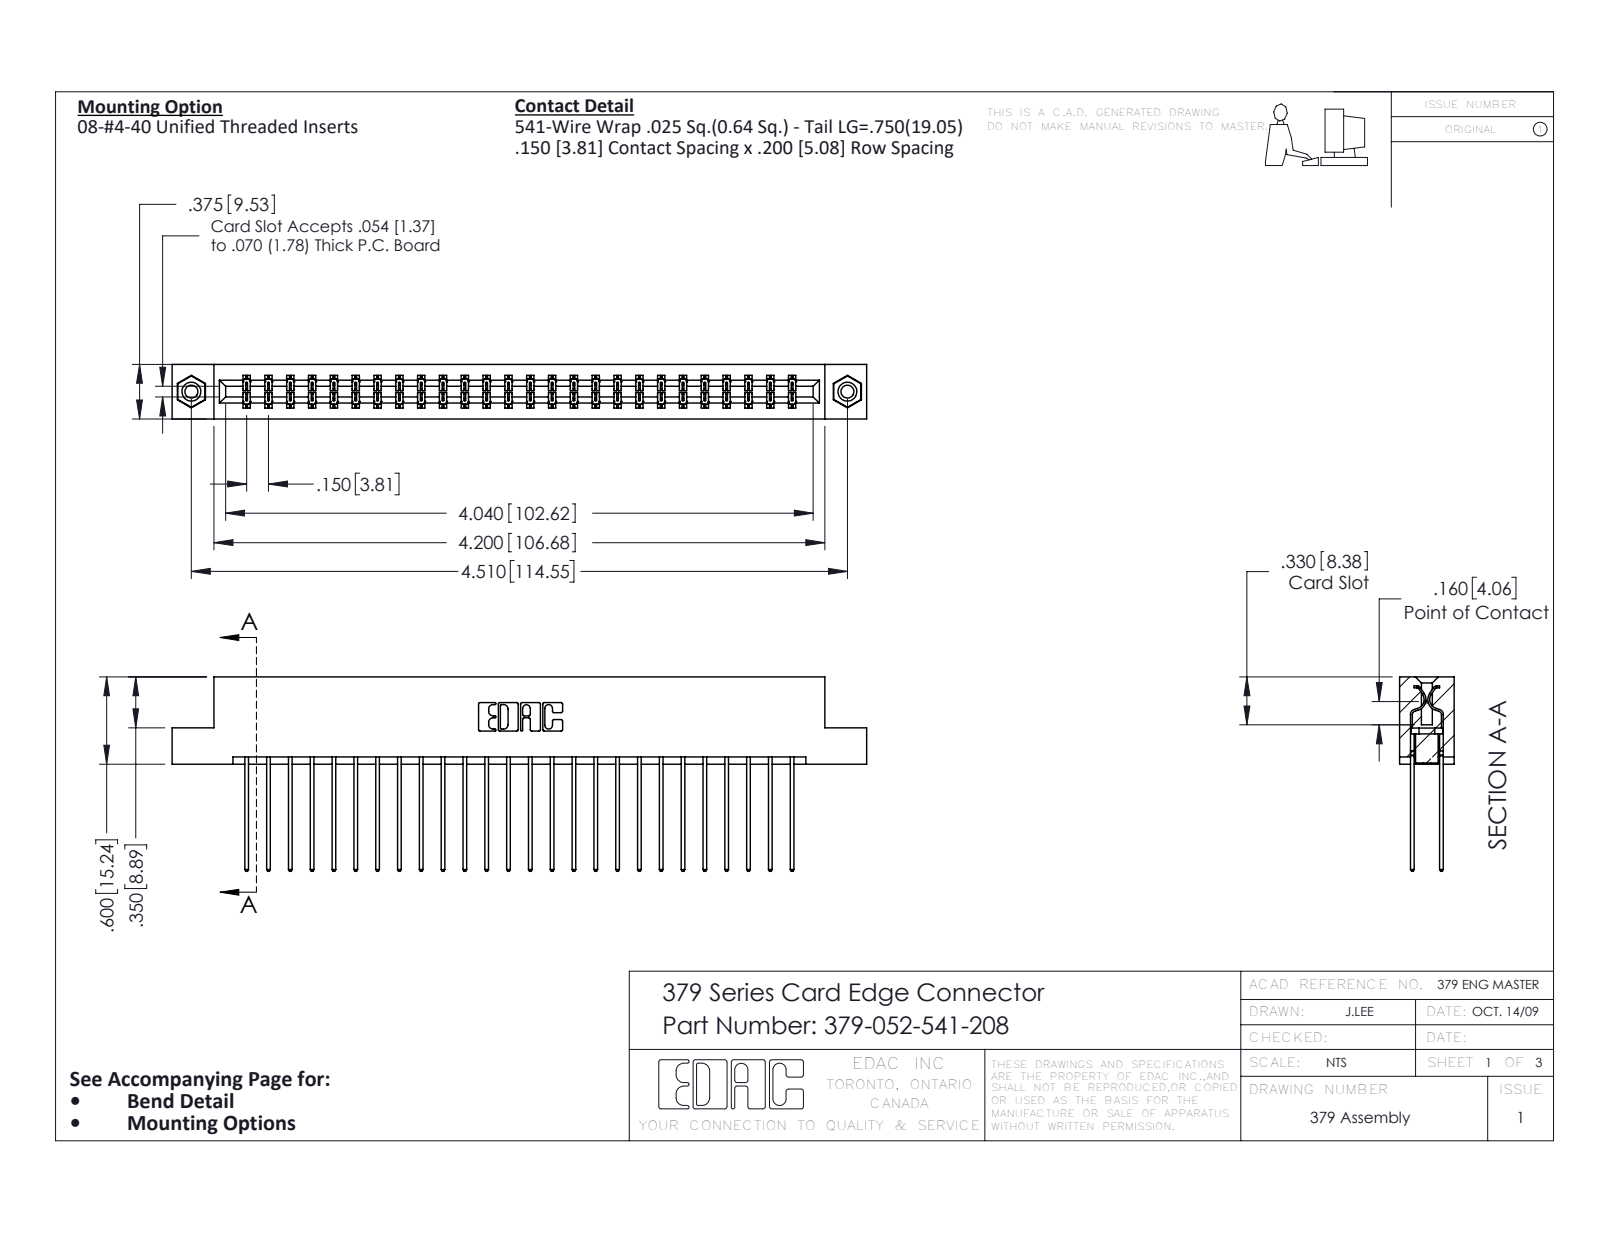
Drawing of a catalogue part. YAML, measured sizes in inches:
part_name: "379 Part_Flush - .156 Dia - TI; 345-250-001_345-250-003-102; 379-052-541-208; 345-292-001_345-293-141"
step_written_by: "SolidWorks 2016 (CONFIG_CONTROL_DESIGN)"
units: inches
bodies: {solids: 55, faces: 2878, planar: 1974, cylindrical: 888, other: 16}
overall_size: [4.775, 1.337, 0.375]
volume: 0.794
surface_area: 24.79
round_holes:
  - {diameter: 0.089, count: 2}
  - {diameter: 0.125, count: 2}
  - {diameter: 0.156, count: 2}
round_bosses_or_shafts:
  - {diameter: 0.155, count: 2}
partial_cylinders:
  - {radius: 0.006, count: 78}
  - {radius: 0.01, count: 52}
  - {radius: 0.01, count: 22}
  - {radius: 0.007, count: 6}
  - {radius: 0.031, count: 6}
  - {radius: 0.026, count: 3}
  - {radius: 0.014, count: 2}
  - {radius: 0.022, count: 2}
face_to_face_distances: [0.3, 0.075, 0.1, 0.2, 0.375, 0.275, 0.025, 0.076, 0.15, 0.225]
hole_center_spacings: [4.51]
